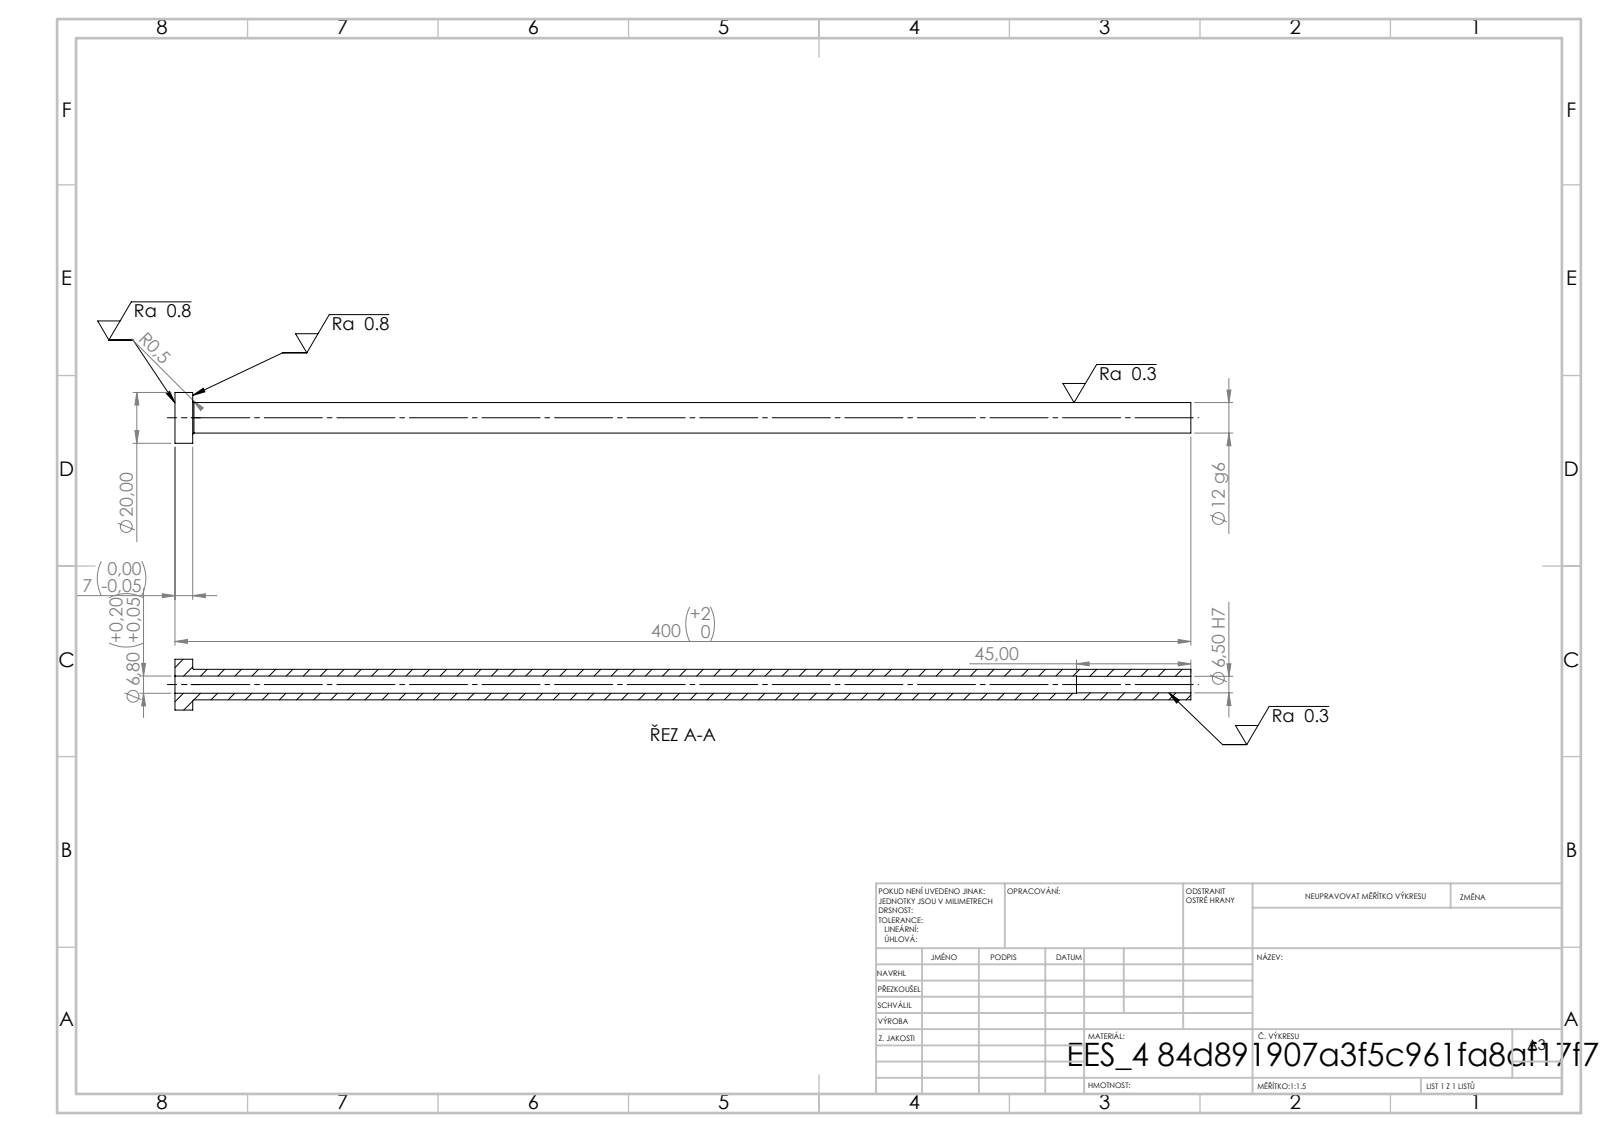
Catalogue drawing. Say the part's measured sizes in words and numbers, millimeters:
Its 3-D file was written by "SolidWorks 2019 (CONFIG_CONTROL_DESIGN)". It is 1 solid with 14 faces: 4 planar, 8 cylindrical and 2 other. Overall it measures 400 by 20 by 20 millimeters. Its volume is 32 263 cubic millimeters and its surface area 24 312 square millimeters. Round holes: 1 of diameter 6.5, 1 of diameter 6.8. Round bosses or shafts: 1 of diameter 20, 1 of diameter 12. The main face-to-face distances are 7, 400, 393, 355, 348, 45.
